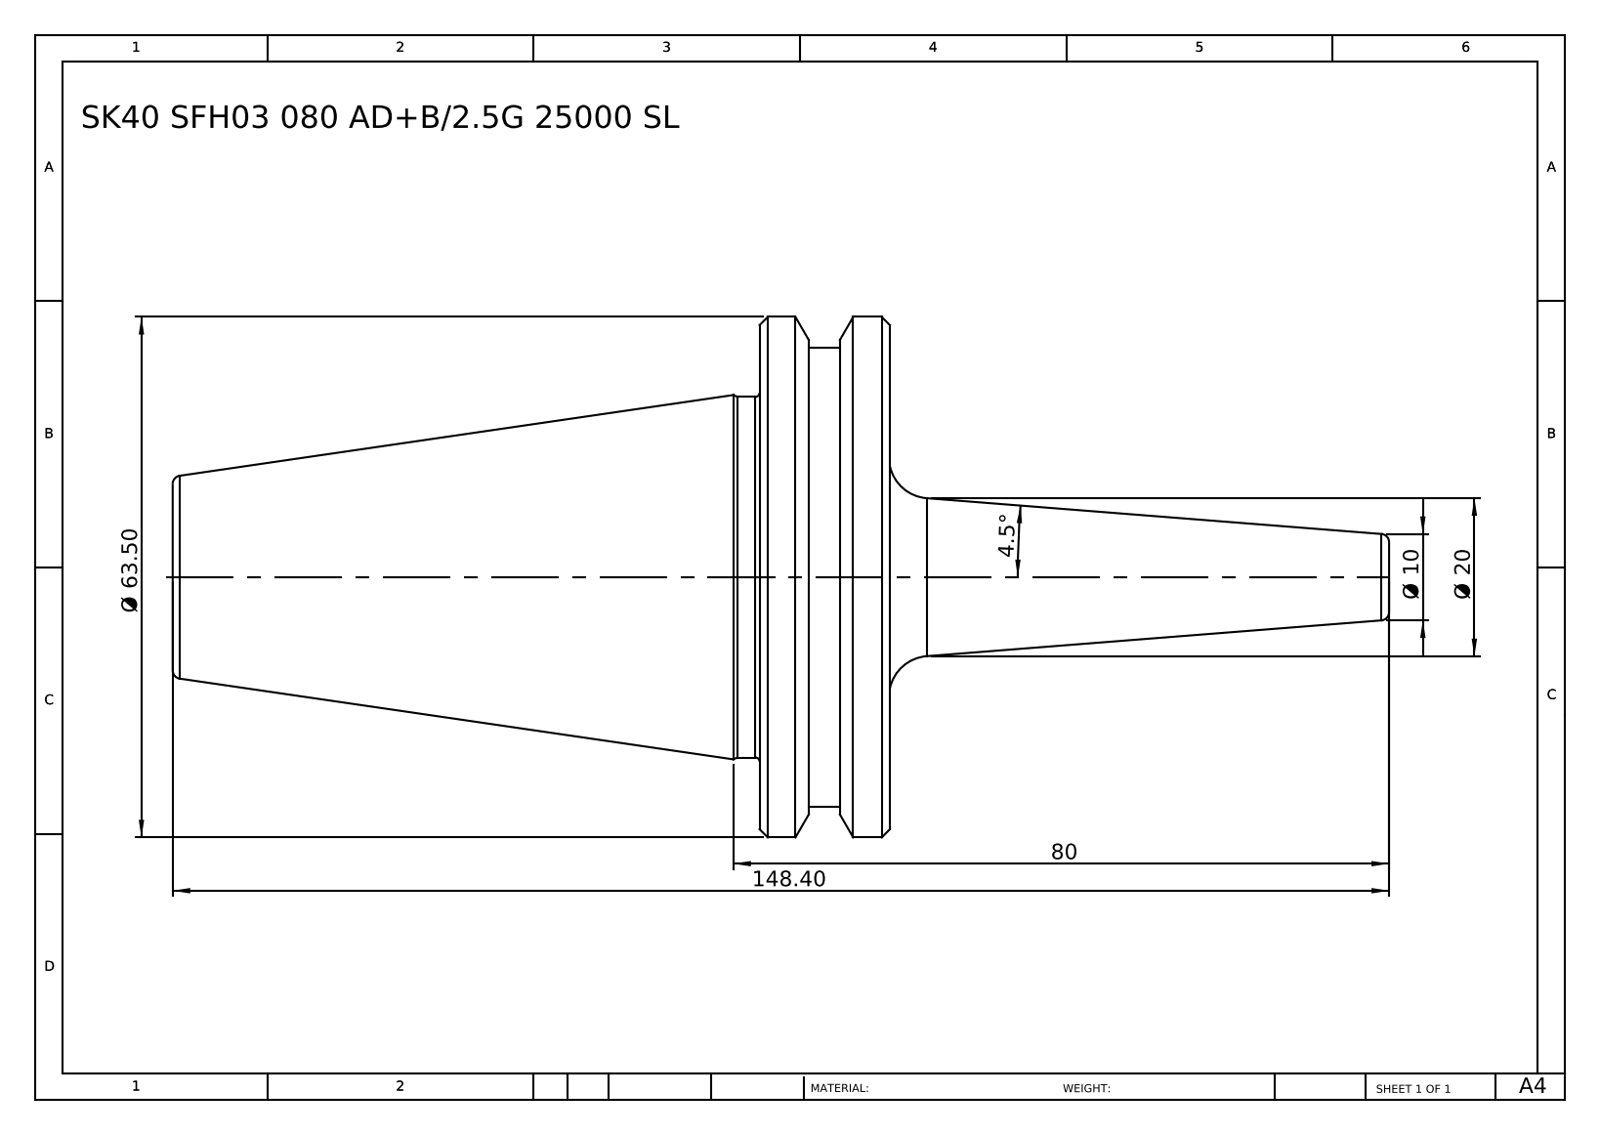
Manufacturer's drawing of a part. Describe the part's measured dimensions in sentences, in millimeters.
The part is named "SK40 SFH03 080 AD+B-2.5G 25000 SL". Its 3-D file was written by "SolidWorks 2014 (CONFIG_CONTROL_DESIGN)". It is 1 solid with 36 faces: 6 planar, 8 cylindrical and 22 other. Overall it measures 148.4 by 63.5 by 63.5 millimeters. Its volume is 128 770 cubic millimeters and its surface area 19 519 square millimeters. Round bosses or shafts: 1 of diameter 63.5, 1 of diameter 56, 1 of diameter 44. The main face-to-face distances are 15.9, 87.5, 71.6, 6.1, 9.8, 81.4, 9.9, 3.8, 6, 77.6.
